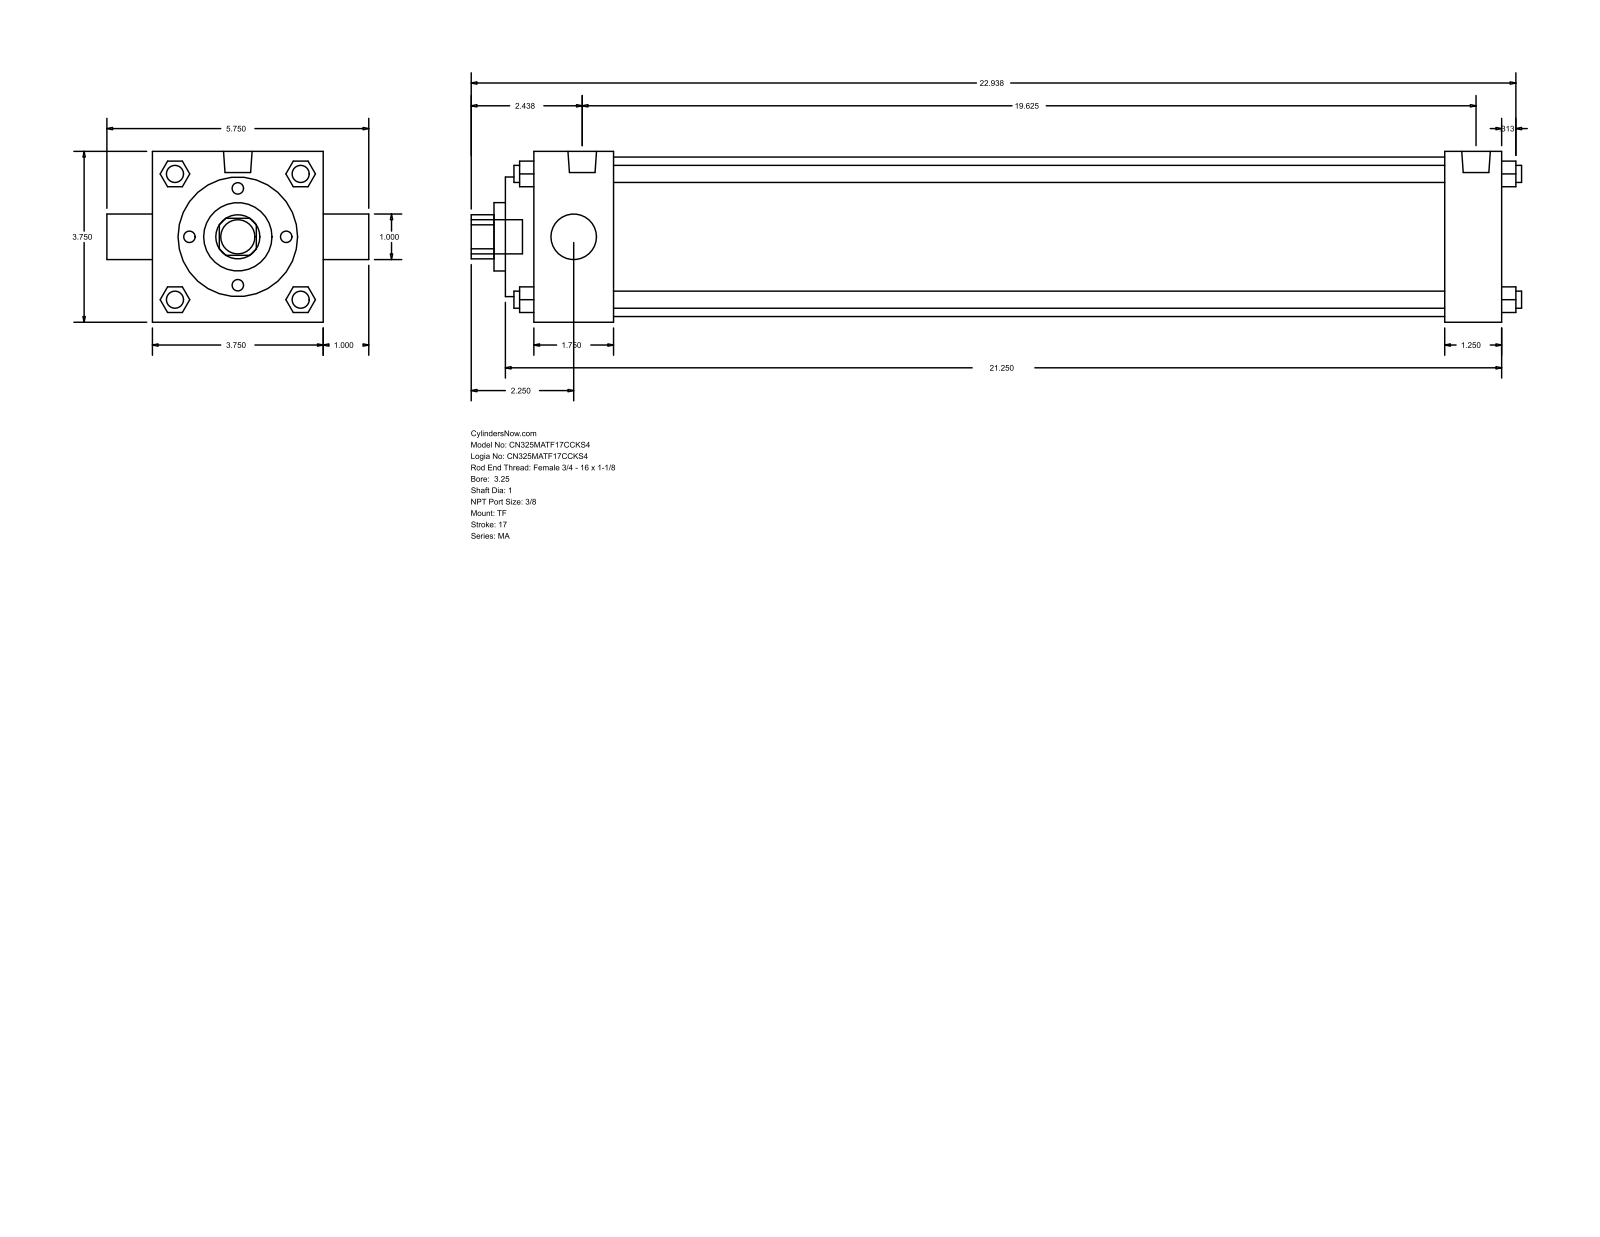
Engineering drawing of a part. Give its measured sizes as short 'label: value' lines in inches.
name: MA_TF__0325_1
written by: GSSL Pune (CONFIG_CONTROL_DESIGN)
unit: in
bodies: 0 solids, 122 faces (93 planar, 29 cylindrical, 0 other)
size: 23.063 × 5.75 × 3.75
holes: 2× ⌀1, 1× ⌀1.5, 1× ⌀2.625, 1× ⌀3.5
bosses: 4× ⌀0.375, 3× ⌀0.437, 2× ⌀0.627, 1× ⌀0.75
rounds: 1× R0.484
face distances: 3.75, 21.25, 21.875, 0.625, 1.75, 20, 18.25, 19.5, 1.25, 2.375
